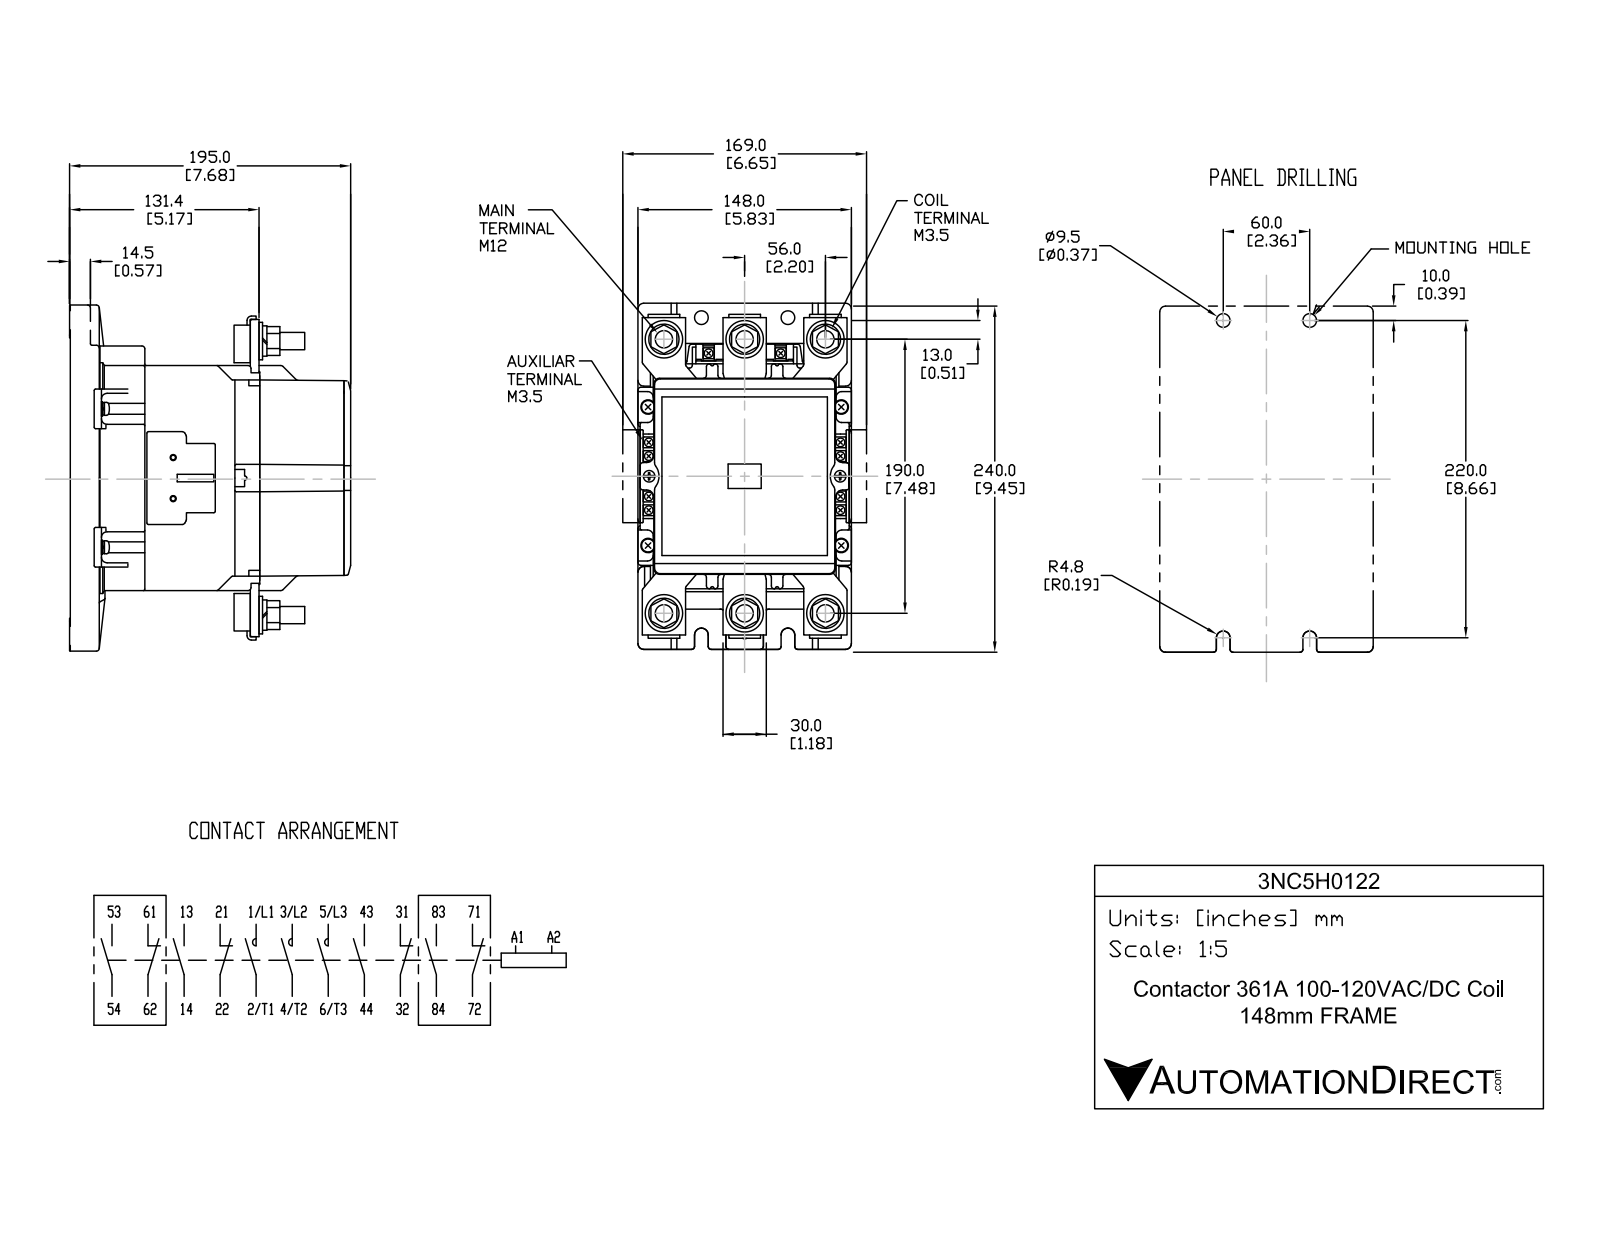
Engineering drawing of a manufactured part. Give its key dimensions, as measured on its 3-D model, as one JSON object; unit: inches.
{"part_name": "3NC5H0122", "step_written_by": "SolidWorks 2018 (AUTOMOTIVE_DESIGN)", "units": "inches", "bodies": {"solids": 20, "faces": 375, "planar": 261, "cylindrical": 114, "other": 0}, "overall_size": [9.449, 7.677, 5.866], "volume_in3": 256.1, "surface_area_in2": 431.1, "round_holes": [[0.472, 6], [0.315, 2], [0.394, 2]], "partial_cylinders_radius": [[0.079, 26], [0.157, 16], [0.039, 12], [0.031, 8], [0.197, 6], [0.02, 2]], "face_to_face_distances": [4.528, 0.433, 4.961, 0.394, 5.748, 5.394, 3.15, 7.677, 0.827, 3.701], "hole_center_spacings": [2.244, 3.765, 4.6, 6.181, 7.81, 7.48, 1.213, 1.324]}
